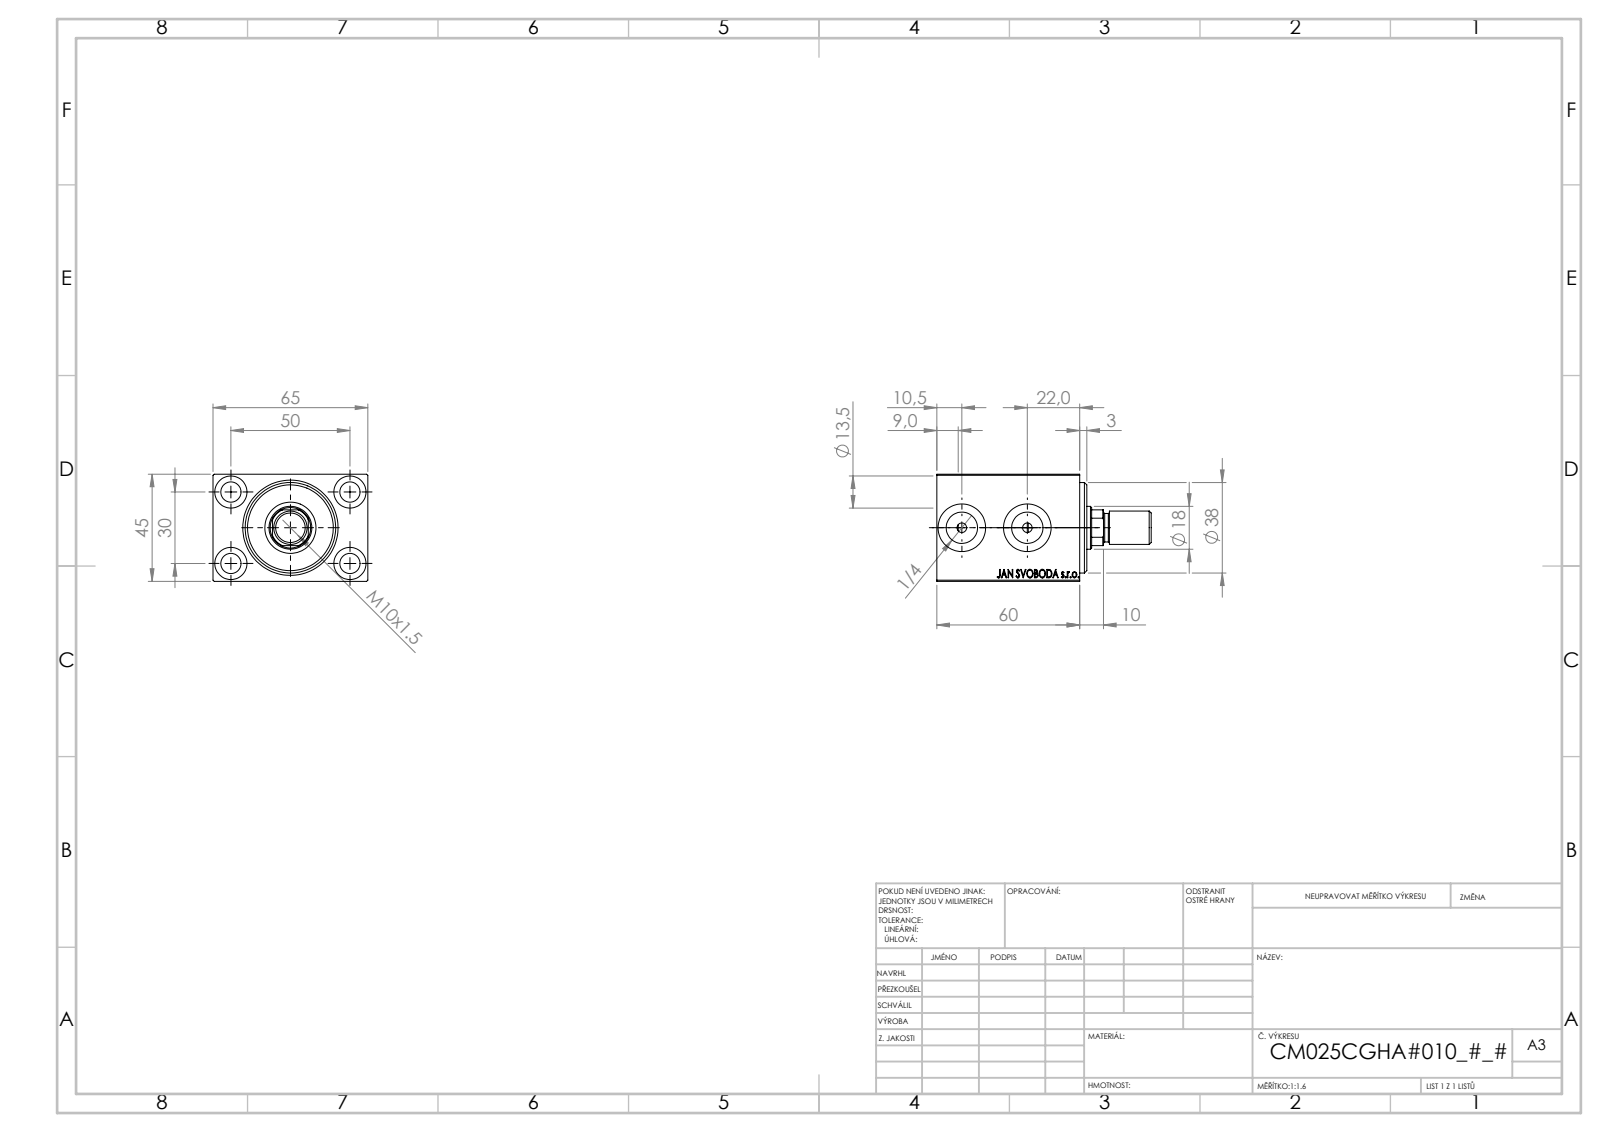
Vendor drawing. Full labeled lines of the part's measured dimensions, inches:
Part name (STEP PRODUCT): V450CM_VC_B; V450CM_C_Body; V450CM_C_VCP; V450CM_MALE_METRIC
STEP written by: SolidWorks 2019 (CONFIG_CONTROL_DESIGN)
Units: inches
Bodies: 4 solids, 876 faces (412 planar, 64 cylindrical, 400 other)
Overall size (bounding box): 3.543 × 2.559 × 1.772
Volume: 9.532 in³ · Surface area: 67.45 in²
Round holes (diameter × count): ⌀0.335 ×5, ⌀0.531 ×4, ⌀0.157 ×2, ⌀0.518 ×2, ⌀0.787 ×2, ⌀0.709 ×1, ⌀0.846 ×1, ⌀0.984 ×1, ⌀1.063 ×1, ⌀1.496 ×1
Round bosses / shafts (diameter × count): ⌀0.551 ×1, ⌀0.472 ×1
Partial cylindrical surfaces — rounded edges, fillets, slot ends (radius × count): R0.335 ×1
Main face-to-face distances: 1.772, 2.559, 0.354, 2.008, 0.197, 2.165, 1.811, 2.362, 0.315, 0.118
Hole centre spacings: 1.148, 1.181, 1.969, 2.296, 1.083
